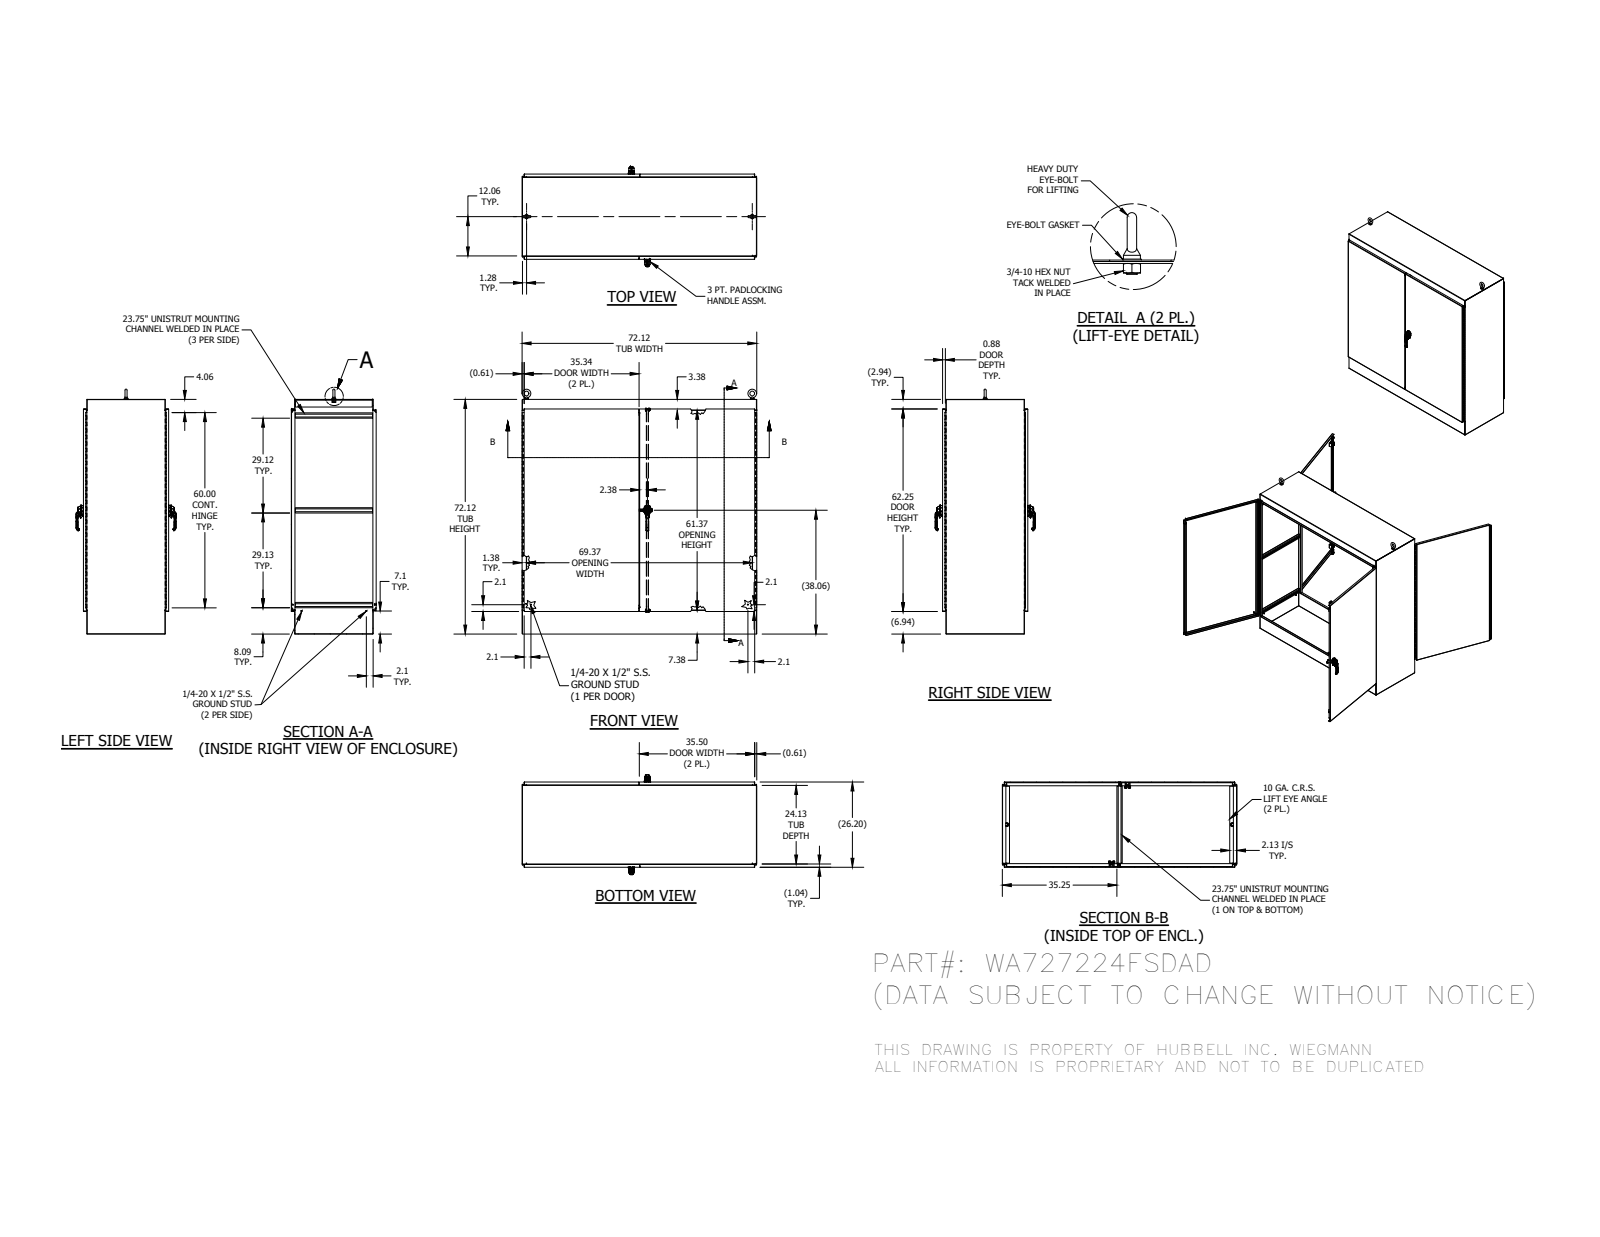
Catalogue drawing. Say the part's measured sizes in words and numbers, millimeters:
The part is named "FUN00103; HFW3025; 316298; 349132 (+8 more)". Its 3-D file was written by "Autodesk Inventor 2014 (AUTOMOTIVE_DESIGN)". It is 110 solids with 7244 faces: 3406 planar, 2450 cylindrical and 1388 other. Overall it measures 1911.29 by 1831.97 by 780.62 millimeters. Its volume is 34 030 000 cubic millimeters and its surface area 27 800 000 square millimeters. Round holes: 16 of diameter 7.02, 8 of diameter 5.08, 6 of diameter 5.4, 6 of diameter 6, 6 of diameter 7.11, 4 of diameter 3.17, 4 of diameter 6.13, 4 of diameter 6.35, 4 of diameter 6.41, 4 of diameter 10.16, 4 of diameter 10.33, 4 of diameter 10.5. Round bosses or shafts: 8 of diameter 6.35, 4 of diameter 25.4, 4 of diameter 14.29, 4 of diameter 13.37, 4 of diameter 12.7, 4 of diameter 9.52, 4 of diameter 8.56, 4 of diameter 7.94. Partial cylindrical surfaces (rounded edges, fillets, slot ends): 360 of radius 0.5, 169 of radius 0.3, 46 of radius 0.79, 41 of radius 0.47, 32 of radius 0.25, 30 of radius 2, 30 of radius 3.17, 29 of radius 3. The main face-to-face distances are 2.38, 662.99, 1829.6, 660.61, 665.37, 26.3, 636.69, 1827.22, 1831.98, 639.07. The hole center spacings are 6.5, 12.5, 22.5, 51.5, 124.7, 126.71, 981.95, 9.66.
